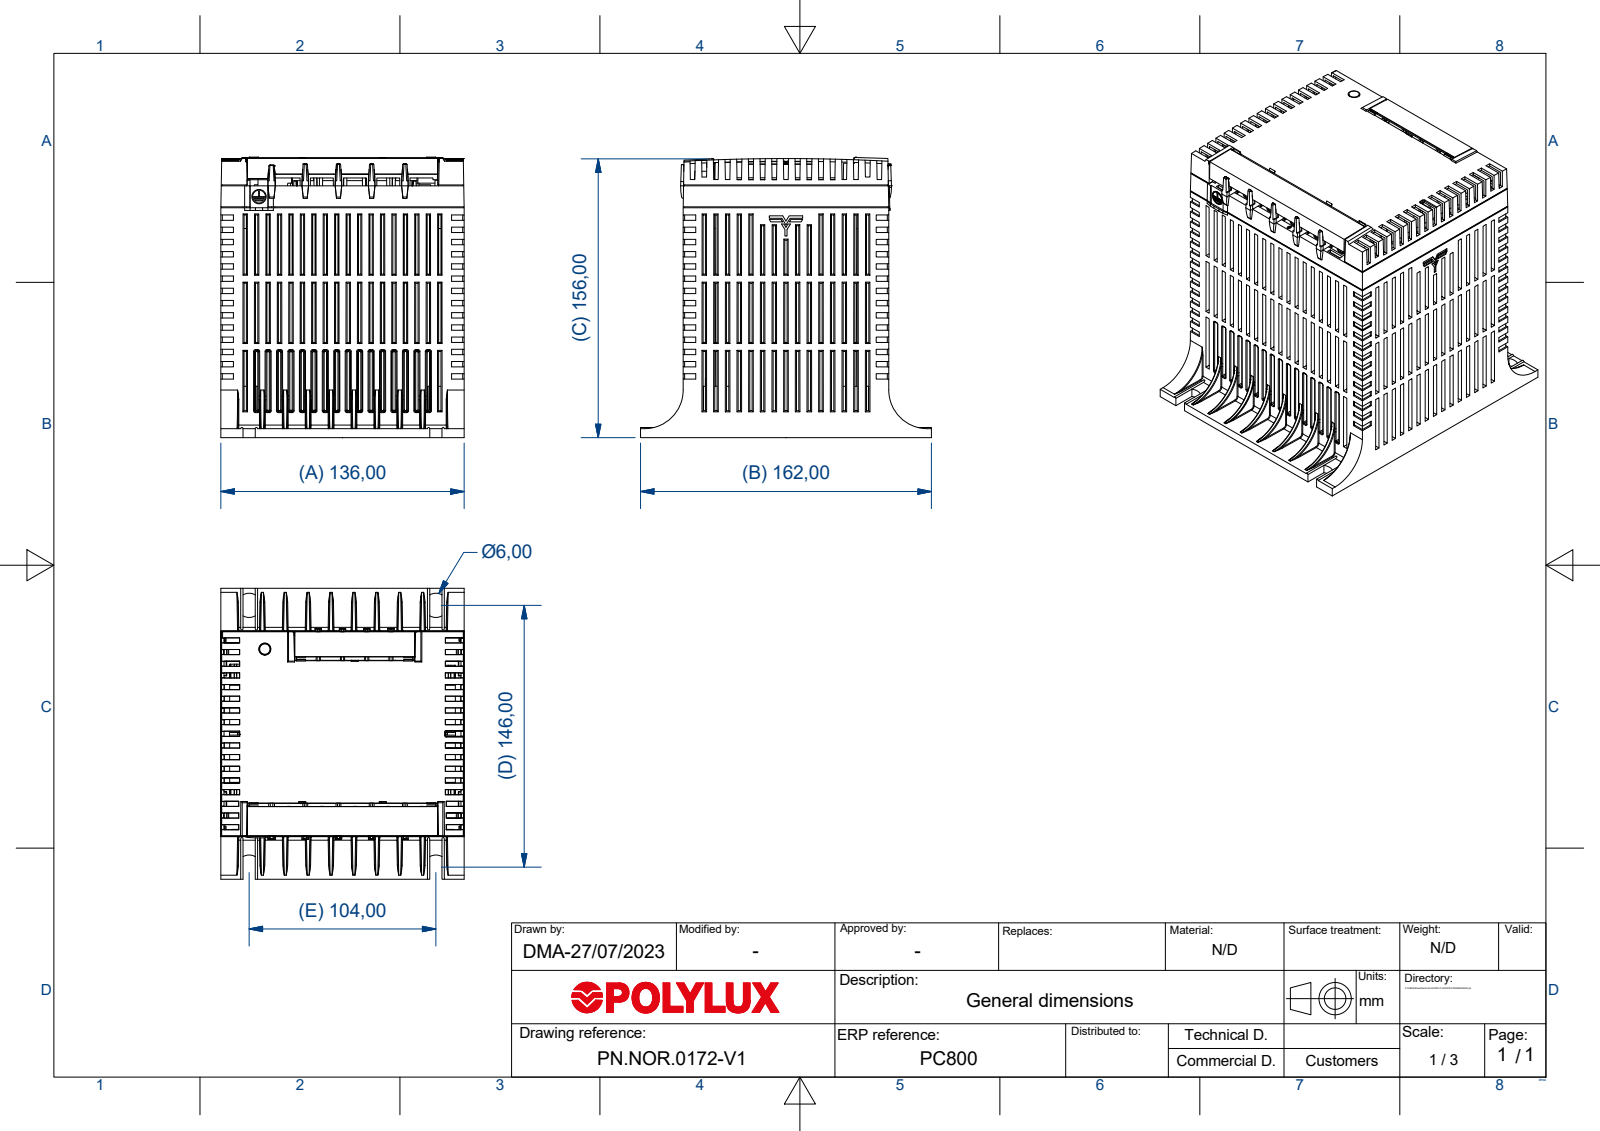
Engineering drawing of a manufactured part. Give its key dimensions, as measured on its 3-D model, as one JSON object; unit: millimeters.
{"part_name": "RC42", "step_written_by": "Autodesk Inventor 2018 (AUTOMOTIVE_DESIGN)", "units": "millimeters", "bodies": {"solids": 0, "faces": 3372, "planar": 2251, "cylindrical": 542, "other": 579}, "overall_size": [162, 156.28, 135.5], "round_holes": [[7.2, 1], [20, 1]], "round_bosses_or_shafts": [[8, 1]], "partial_cylinders_radius": [[0.5, 235], [0.35, 72], [0.2, 24], [0.71, 12], [0.65, 4], [0.4, 2], [0.7, 2], [1, 2]], "face_to_face_distances": [6.28, 3.8, 12.56, 18.84, 6.4, 25.61, 135.5, 114.5, 25.12, 19.21]}
